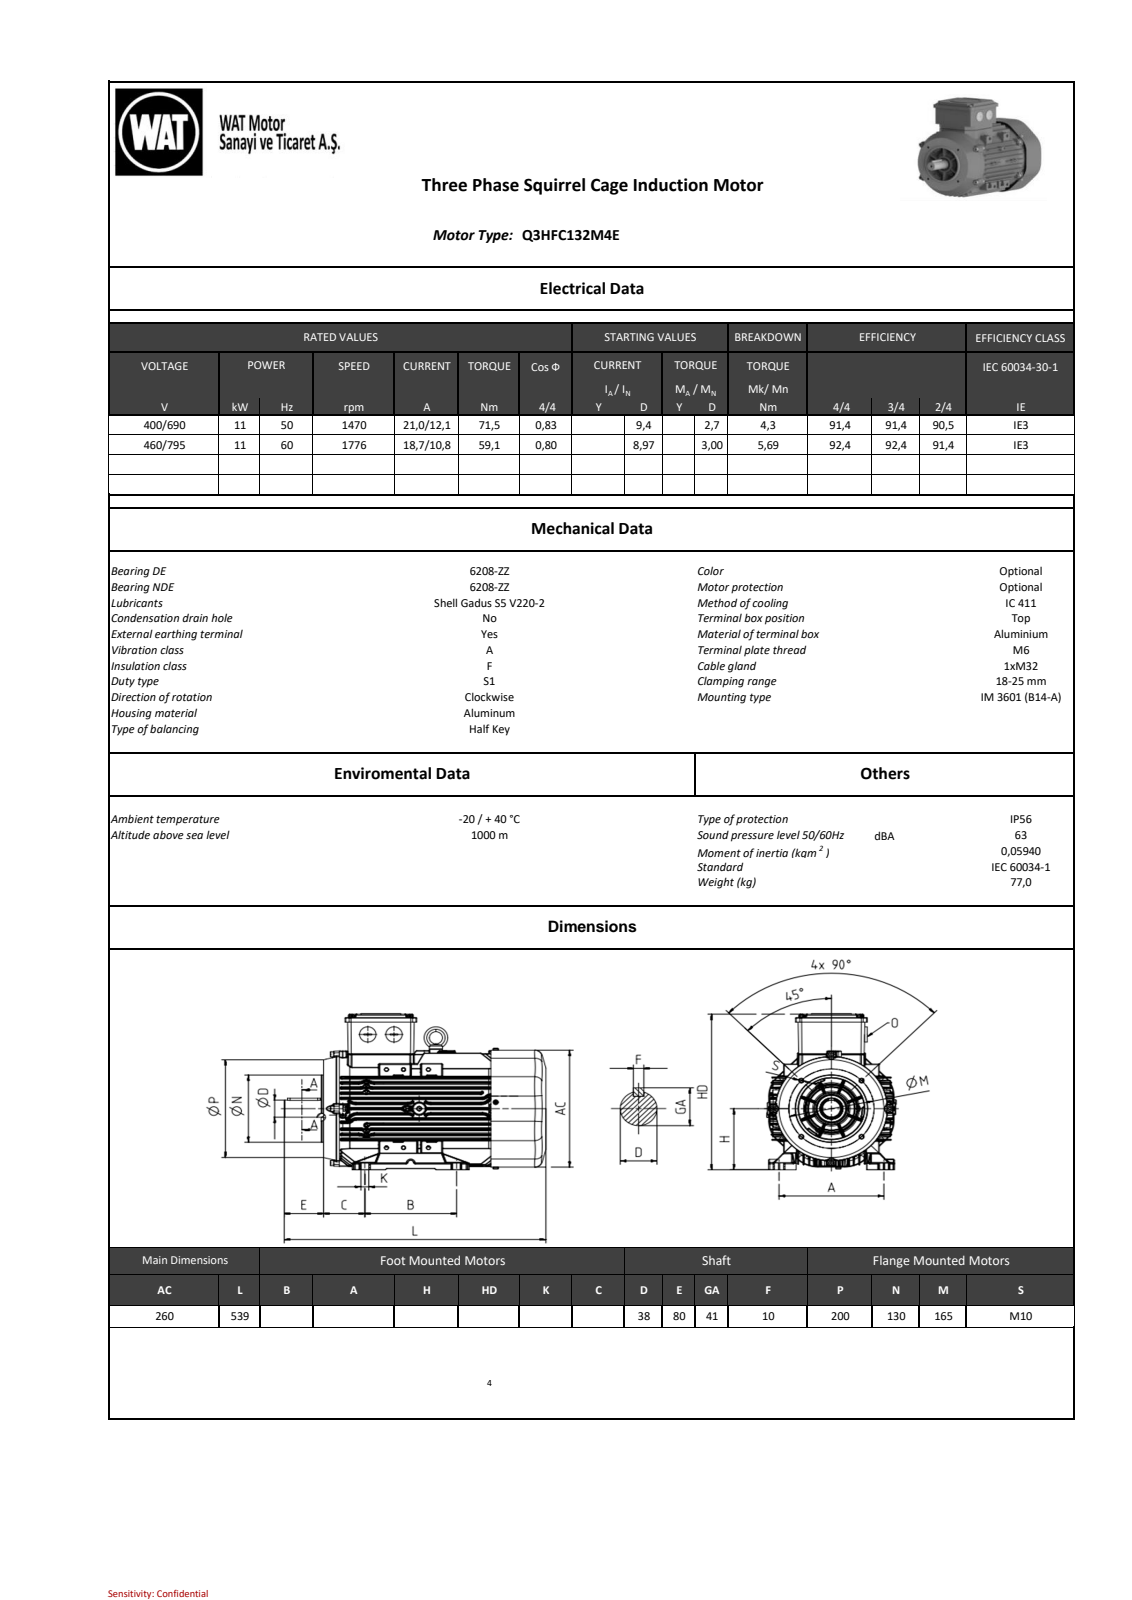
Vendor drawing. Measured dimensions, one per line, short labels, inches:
name: QH series_ 132_B14a _DEEP COVER__stp_objects
written by: SIEMENS PLM Software NX2206.8101 (AP203_CONFIGURATION_CONTROLLED_3D_DESIGN_OF_MECHANICAL_PARTS_AND_ASSEMBLIES_MIM_LF)
unit: in
bodies: 0 solids, 7491 faces (1867 planar, 3159 cylindrical, 2465 other)
size: 21.219 × 12.629 × 10.541
holes: 2× ⌀0.333, 2× ⌀0.334, 1× ⌀0.315, 1× ⌀0.316, 1× ⌀0.334, 1× ⌀0.472, 1× ⌀0.512, 1× ⌀1.358, 1× ⌀2.441, 1× ⌀3.228, 1× ⌀7.087, 1× ⌀8.858
bosses: 9× ⌀0.315, 4× ⌀0.512, 3× ⌀1.496, 1× ⌀9.075, 1× ⌀5.118, 1× ⌀3.416, 1× ⌀1.575, 1× ⌀1.472
rounds: 1011× R0.031, 877× R0.039, 64× R0.118, 61× R0.02, 61× R0.079, 58× R0.059, 18× R0.197, 16× R2.362
face distances: 0.41, 0.059, 0.416, 0.405, 0.82, 4.944, 4.535, 4.13, 3.719, 0.831
hole spacings: 4.494, 0.026, 0.689, 3.517, 4.088, 4.098, 4.482, 4.921
